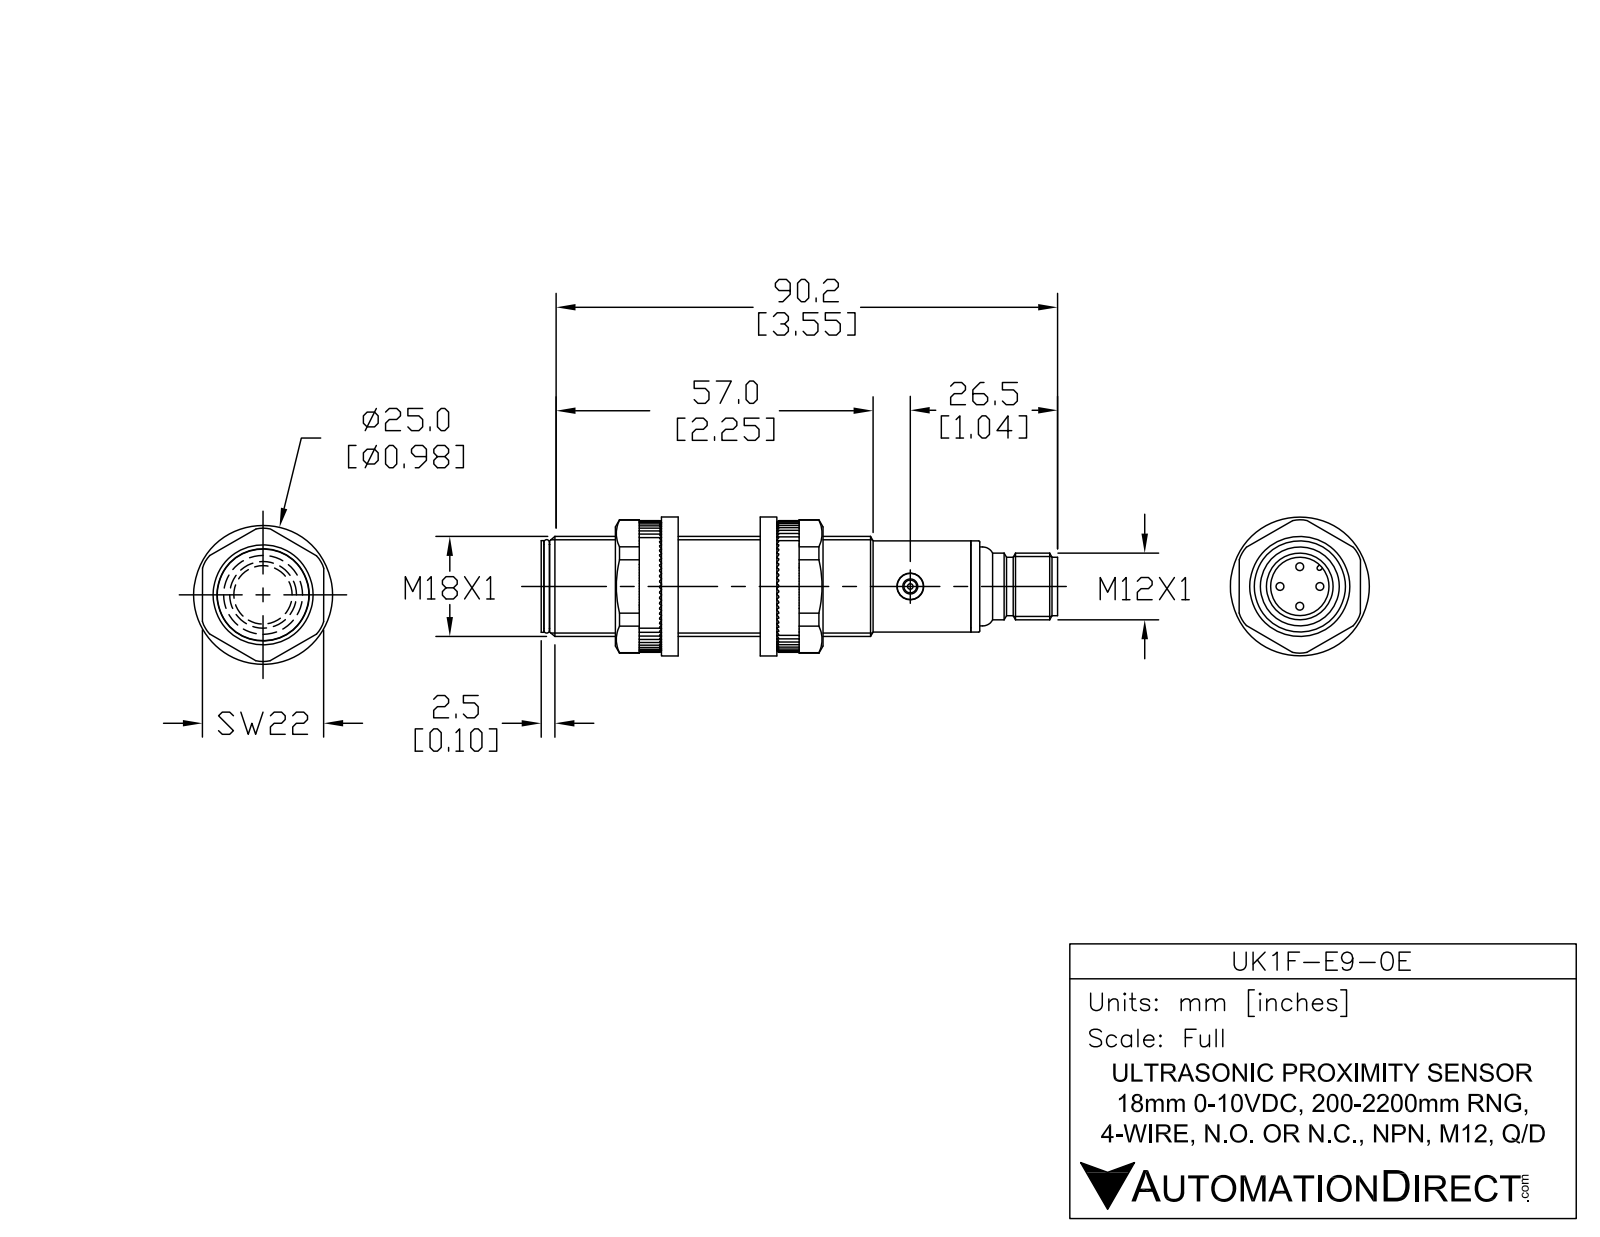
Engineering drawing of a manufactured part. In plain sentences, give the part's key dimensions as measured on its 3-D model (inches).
The part is named "UK1F-E9-0E". Its 3-D file was written by "SolidWorks 2017 (AUTOMOTIVE_DESIGN)". It is 6 solids with 106 faces: 21 planar, 48 cylindrical and 37 other. Overall it measures 3.606 by 0.709 by 0.709 inches. Its volume is 1.202 cubic inches and its surface area 10.68 square inches. Round holes: 1 of diameter 0.106, 1 of diameter 0.185, 1 of diameter 0.276, 1 of diameter 0.327, 1 of diameter 0.374. Round bosses or shafts: 4 of diameter 0.039, 1 of diameter 0.709, 1 of diameter 0.654, 1 of diameter 0.646, 1 of diameter 0.622, 1 of diameter 0.559, 1 of diameter 0.472, 1 of diameter 0.413. Partial cylindrical surfaces (rounded edges, fillets, slot ends): 1 of radius 0.024. The main face-to-face distances are 2.957, 0.039, 2.996, 0.037, 2.994, 0.043, 0.157, 3.055, 3.053, 3.016.
